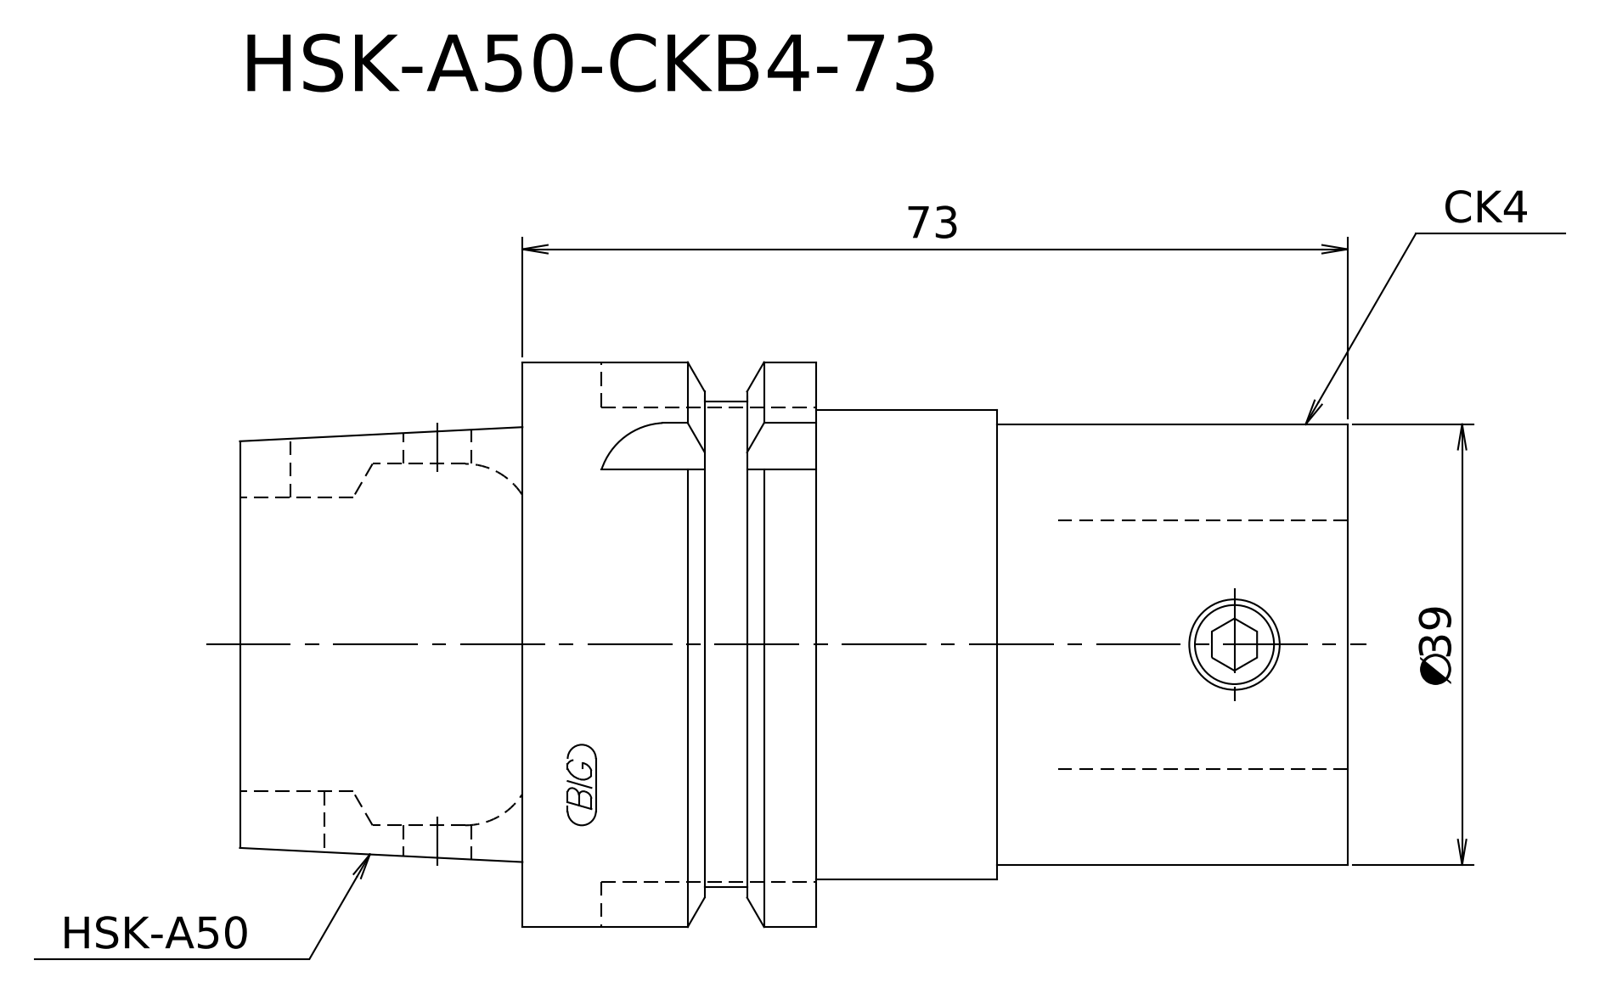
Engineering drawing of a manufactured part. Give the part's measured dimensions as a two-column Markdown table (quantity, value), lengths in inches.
| quantity | value |
| --- | --- |
| STEP written by | Kubotek KeyCreator V8.5.1 (14335) (CONFIG_CONTROL_DESIGN) |
| units | inches |
| bodies | 1 solid, 16 faces (7 planar, 6 cylindrical, 3 other) |
| overall size | 3.858 × 1.969 × 1.969 |
| volume | 8.212 in³ |
| surface area | 26.79 in² |
| round bosses / shafts (diameter × count) | 1.969 × 1, 1.693 × 1, 1.638 × 1, 1.535 × 1, 1.508 × 1 |
| main face-to-face distances | 3.858, 2.874, 0.984, 1.85, 1.024, 2.008, 1.22, 0.63, 1.654, 2.638 |
